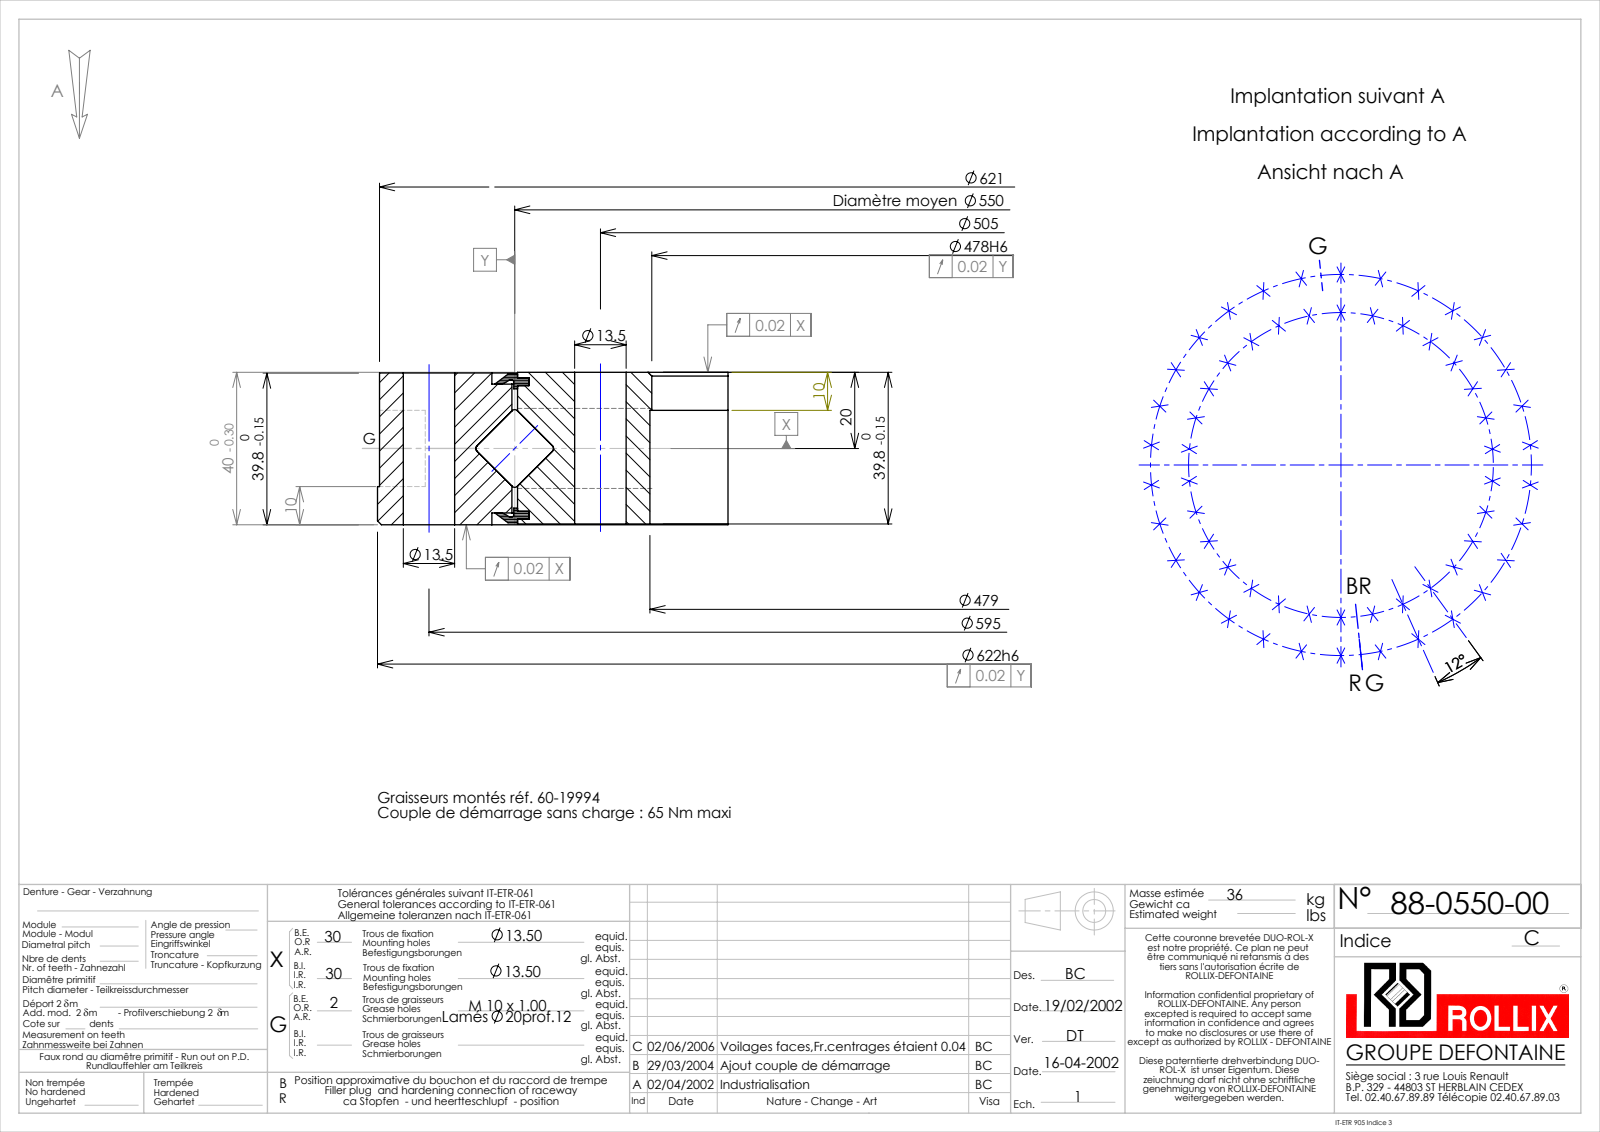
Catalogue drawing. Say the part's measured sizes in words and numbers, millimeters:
The part is named "88-0550-00". Its 3-D file was written by "SolidWorks 2016 (CONFIG_CONTROL_DESIGN)". It is 7 solids with 279 faces: 46 planar, 178 cylindrical and 55 other. Overall it measures 622 by 622 by 40 millimeters. Its volume is 4 093 000 cubic millimeters and its surface area 739 187 square millimeters. Round holes: 60 of diameter 13.5, 2 of diameter 9, 2 of diameter 20, 1 of diameter 478, 1 of diameter 479, 1 of diameter 542.5, 1 of diameter 548.5, 1 of diameter 551.5, 1 of diameter 562. Round bosses or shafts: 2 of diameter 10, 1 of diameter 622, 1 of diameter 621, 1 of diameter 550.5, 1 of diameter 15. The main face-to-face distances are 39.8, 39.6, 40, 3.1, 36.9, 2.9, 36.7, 3.5, 36.5, 3.3. The hole center spacings are 543.56, 582, 442.17, 297.5, 591.74, 242.01, 565.88, 62.19.
